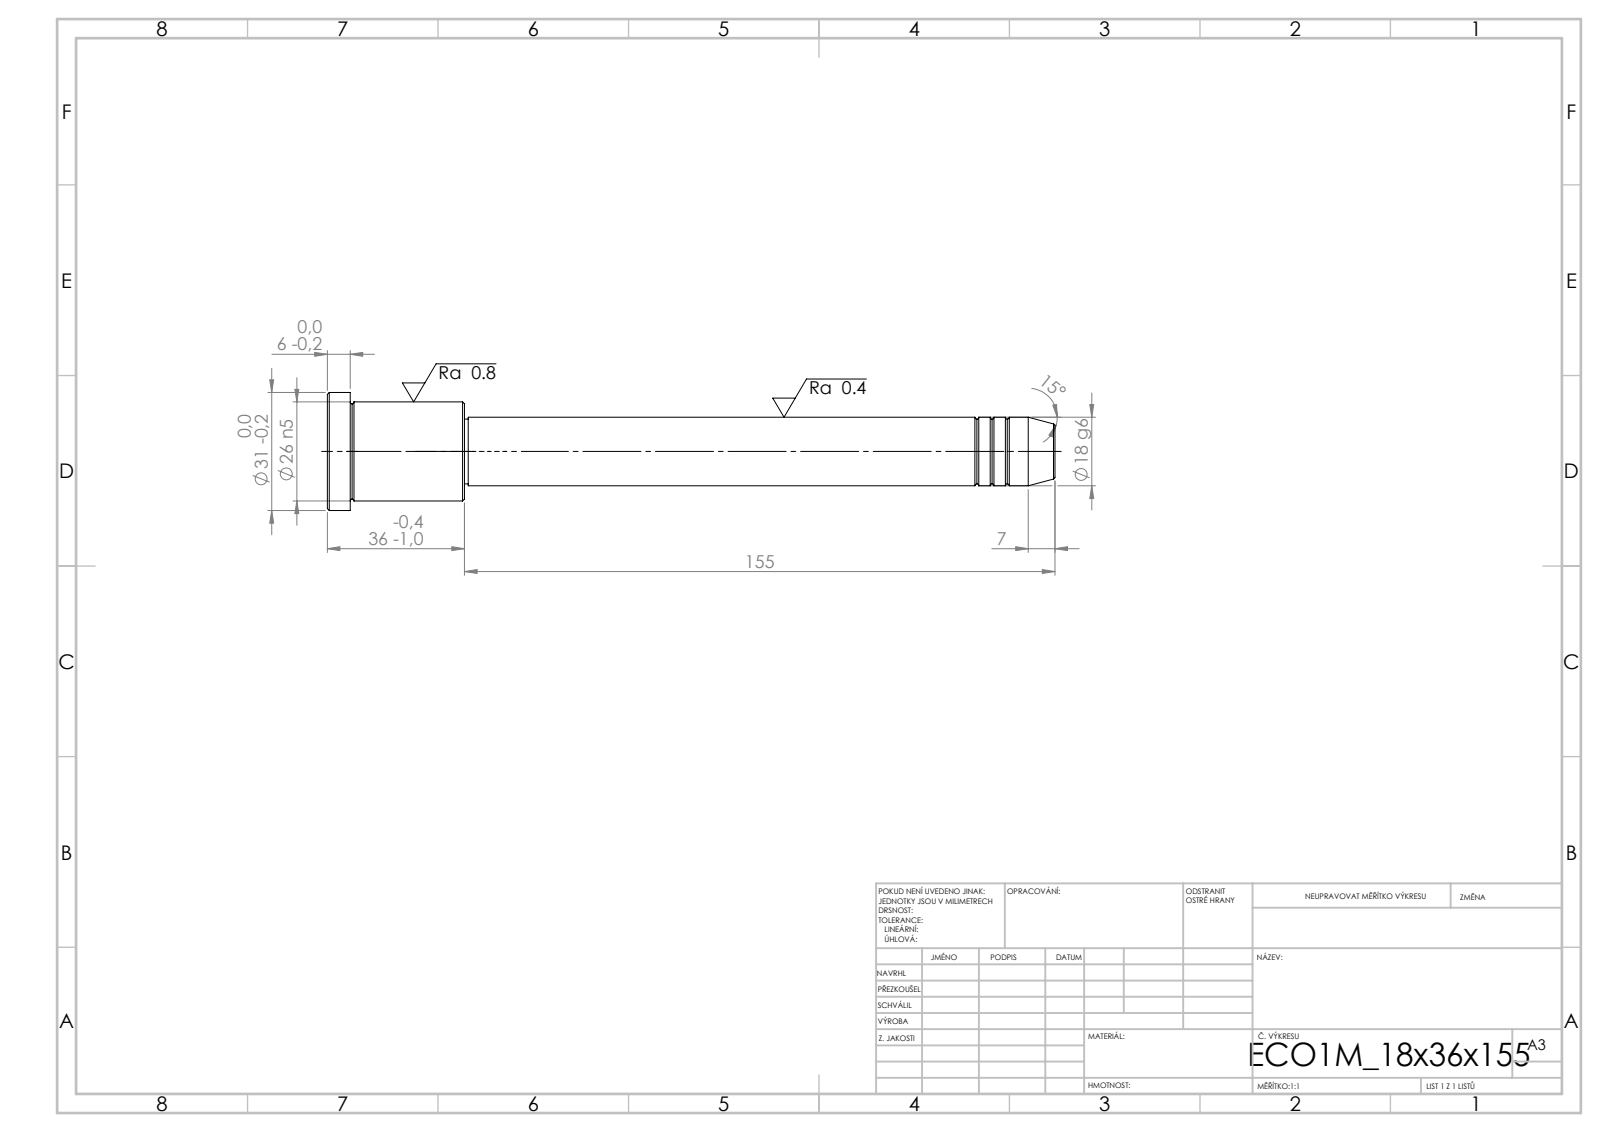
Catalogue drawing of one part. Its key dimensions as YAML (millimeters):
step_written_by: "SolidWorks 2019 (CONFIG_CONTROL_DESIGN)"
units: millimeters
bodies: {solids: 1, faces: 43, planar: 5, cylindrical: 14, other: 24}
overall_size: [191, 31, 31]
volume: 59406
surface_area: 13310
round_bosses_or_shafts:
  - {diameter: 31, count: 1}
  - {diameter: 26, count: 1}
  - {diameter: 18, count: 1}
  - {diameter: 17, count: 1}
face_to_face_distances: [36, 30, 6, 155, 185, 191, 154, 1, 31, 37]
